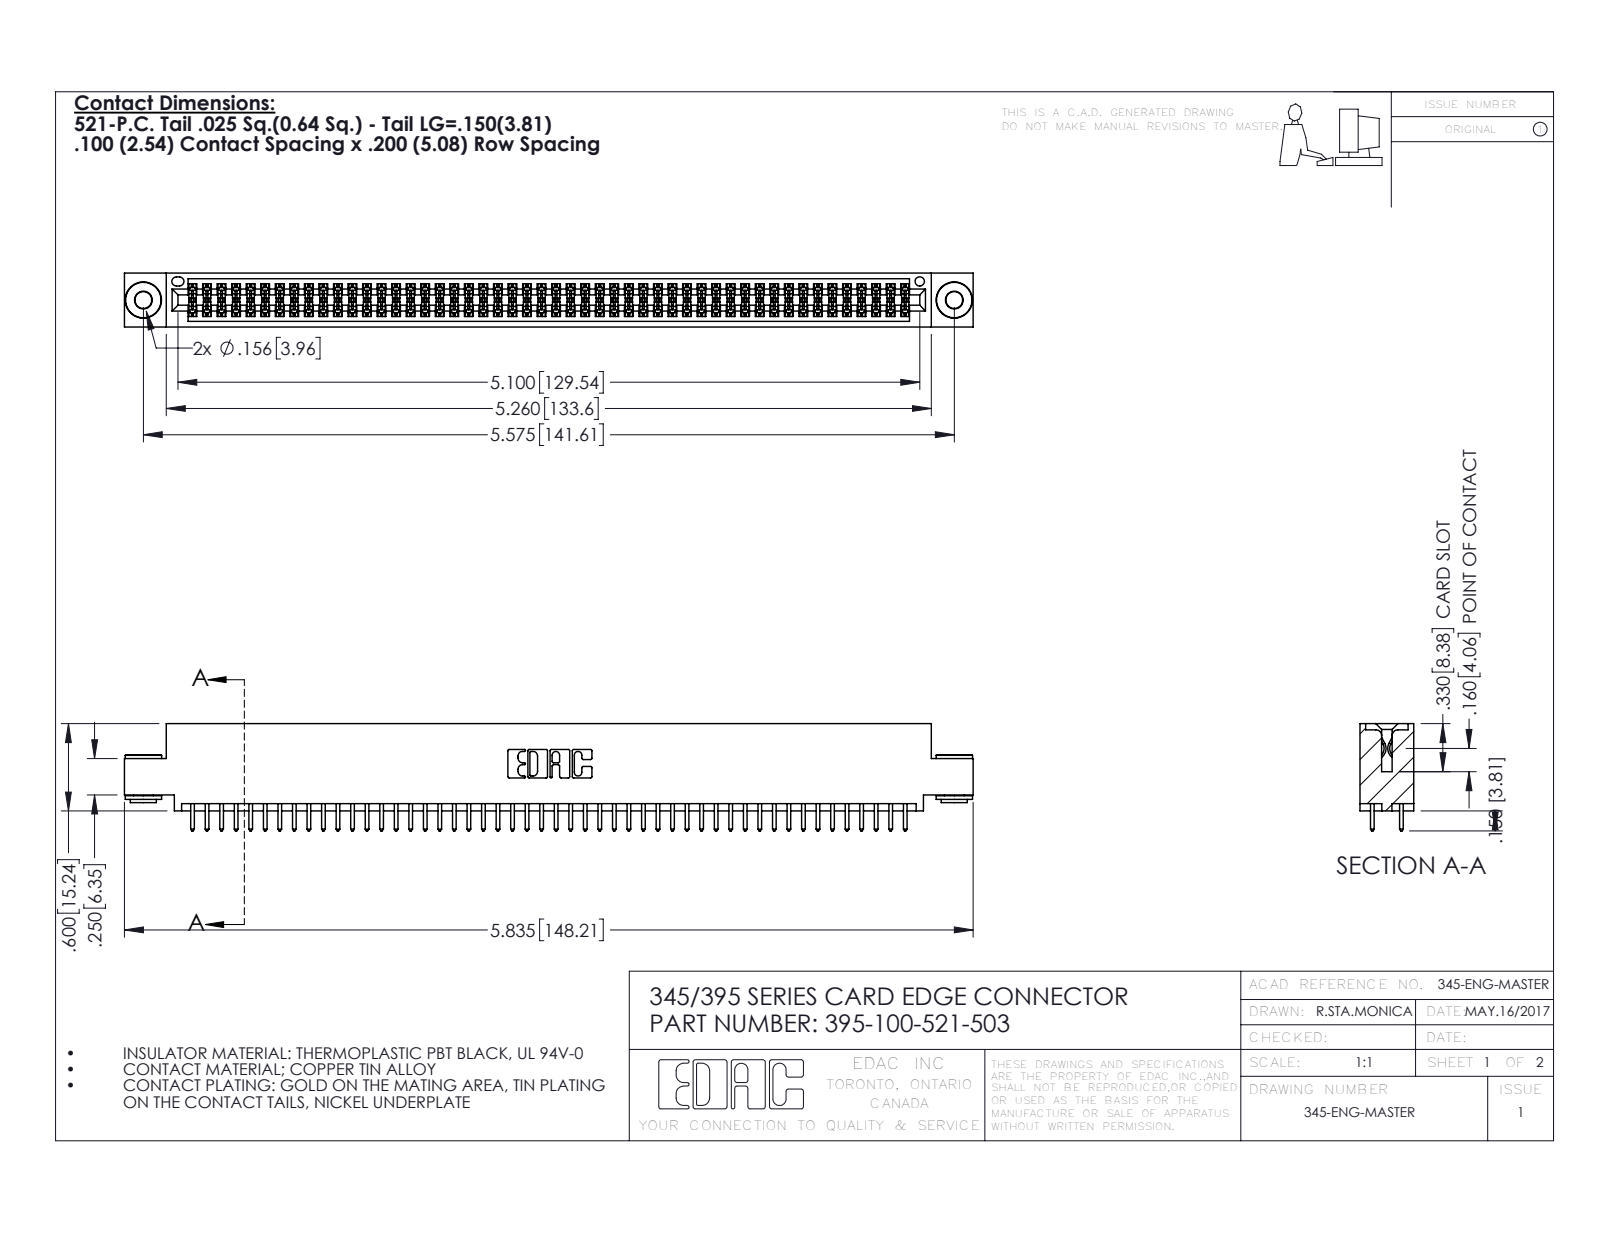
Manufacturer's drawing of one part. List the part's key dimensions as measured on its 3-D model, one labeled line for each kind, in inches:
Part name (STEP PRODUCT): 345 Part_0.110 Offset - 0.156 Dia-TH; 345-250-002_345-250-002-102; 345-292-001_345-293-121; 395-100-521-503
STEP written by: SolidWorks 2016 (CONFIG_CONTROL_DESIGN)
Units: inches
Bodies: 103 solids, 5168 faces (3394 planar, 1766 cylindrical, 8 other)
Overall size (bounding box): 5.835 × 0.737 × 0.37
Volume: 0.877 in³ · Surface area: 33.23 in²
Round holes (diameter × count): ⌀0.116 ×2, ⌀0.156 ×2, ⌀0.064 ×1
Round bosses / shafts (diameter × count): ⌀0.25 ×2, ⌀0.18 ×2, ⌀0.136 ×2
Partial cylindrical surfaces — rounded edges, fillets, slot ends (radius × count): R0.006 ×150, R0.01 ×100, R0.01 ×22, R0.007 ×6, R0.031 ×6, R0.026 ×3, R0.014 ×2, R0.019 ×2
Main face-to-face distances: 0.072, 0.298, 0.2, 0.025, 0.37, 0.098, 0.272, 0.225, 0.175, 0.149
Hole centre spacings: 0.27, 5.339, 5.575
